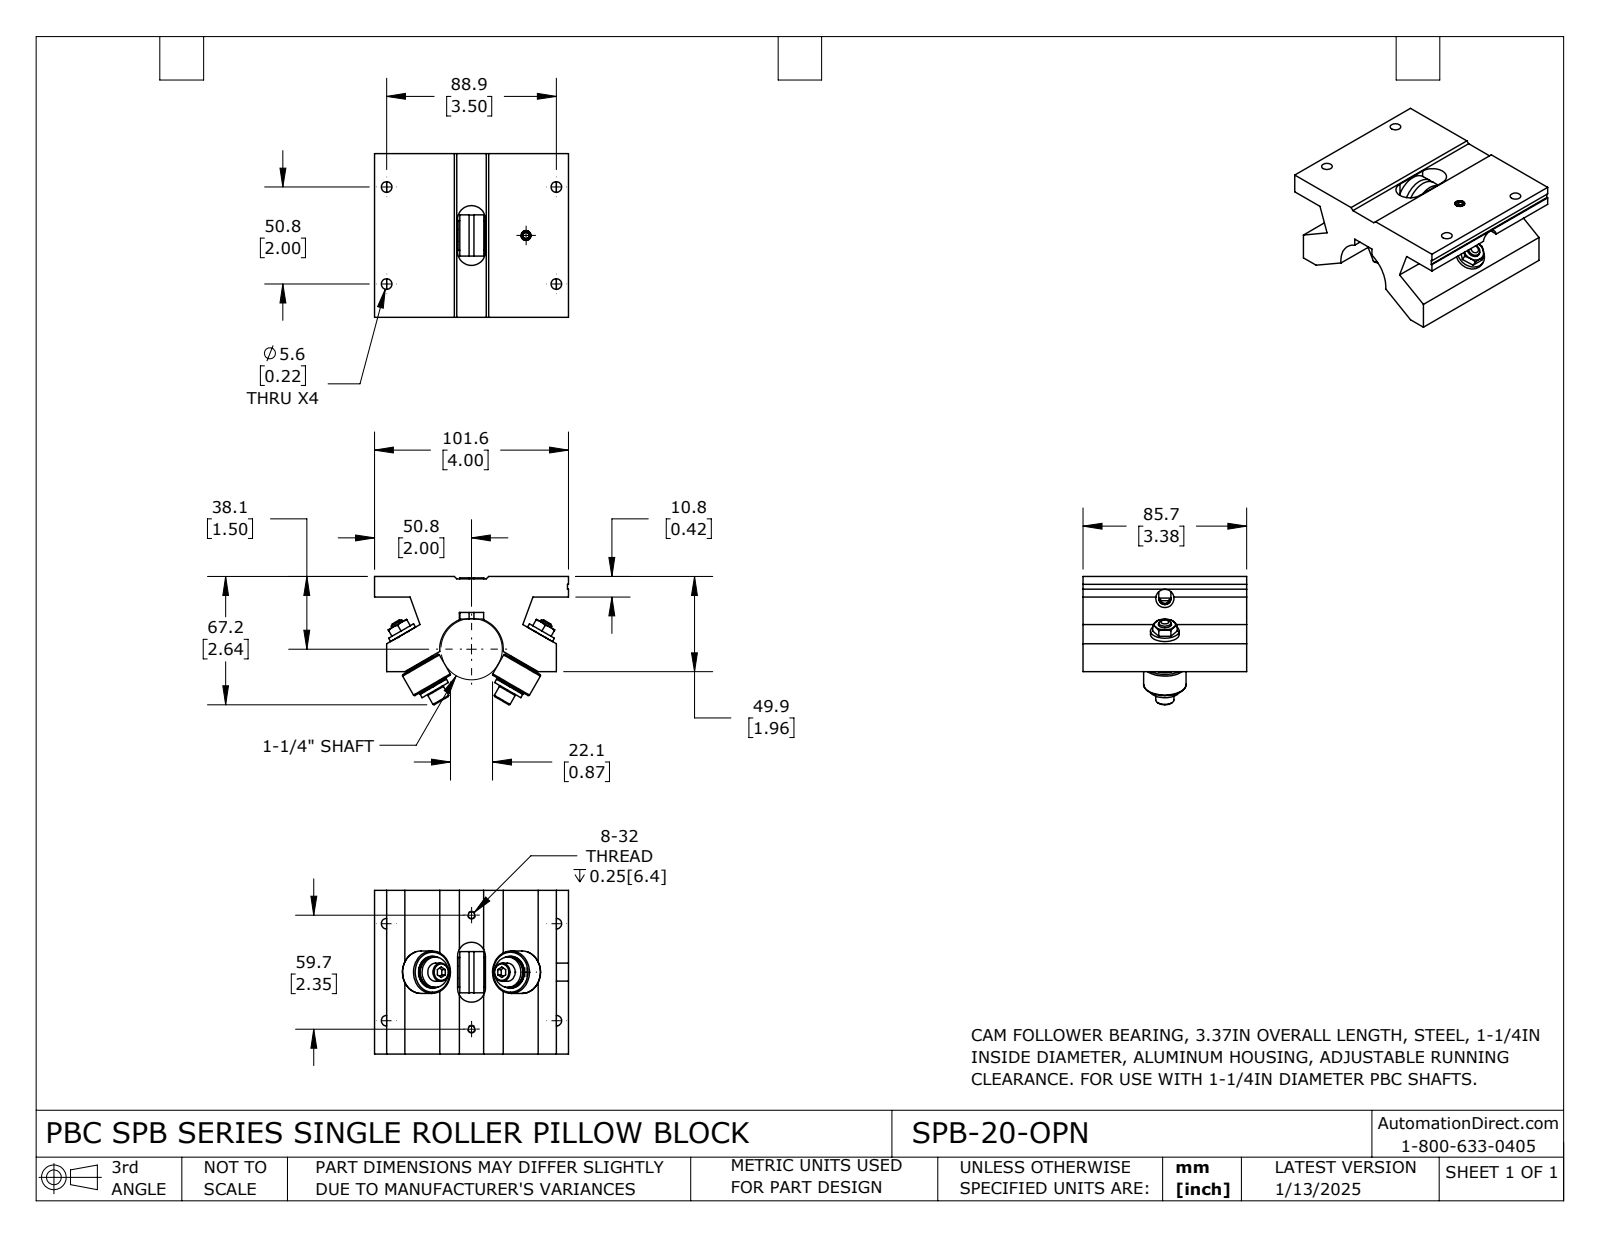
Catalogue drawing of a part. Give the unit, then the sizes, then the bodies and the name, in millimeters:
Units: millimetres
Overall size (bounding box): 101.6 × 85.7 × 67.2
Round holes (diameter × count): ⌀5.6 ×4, ⌀3.5 ×2, ⌀4.7 ×2, ⌀6.4 ×2, ⌀6.4 ×2, ⌀7.1 ×2, ⌀7.3 ×2, ⌀9.7 ×2, ⌀16.4 ×2, ⌀5.1 ×1, ⌀5.6 ×1, ⌀6.3 ×1
Round bosses / shafts (diameter × count): ⌀22.2 ×2, ⌀15.9 ×2, ⌀15.1 ×2, ⌀9.6 ×2, ⌀9.5 ×2, ⌀6.4 ×2, ⌀21.6 ×1, ⌀15.5 ×1
Partial cylindrical surfaces — rounded edges, fillets, slot ends (radius × count): R7.3 ×2, R16.6 ×1
Main face-to-face distances: 17.4, 10.8, 85.7, 6.4, 39.1, 49.9, 95.3, 88.9, 48.6, 9.5
Hole centre spacings: 44.7, 70.9, 30, 41.3, 50.8, 77.3, 88.9, 102.4
Volume: 255 800 mm³ · Surface area: 56 040 mm²
Bodies: 13 solids, 360 faces (123 planar, 122 cylindrical, 115 other)
Part name (STEP PRODUCT): SPB-20-OPN
STEP written by: SolidWorks 2023 (CONFIG_CONTROL_DESIGN)
